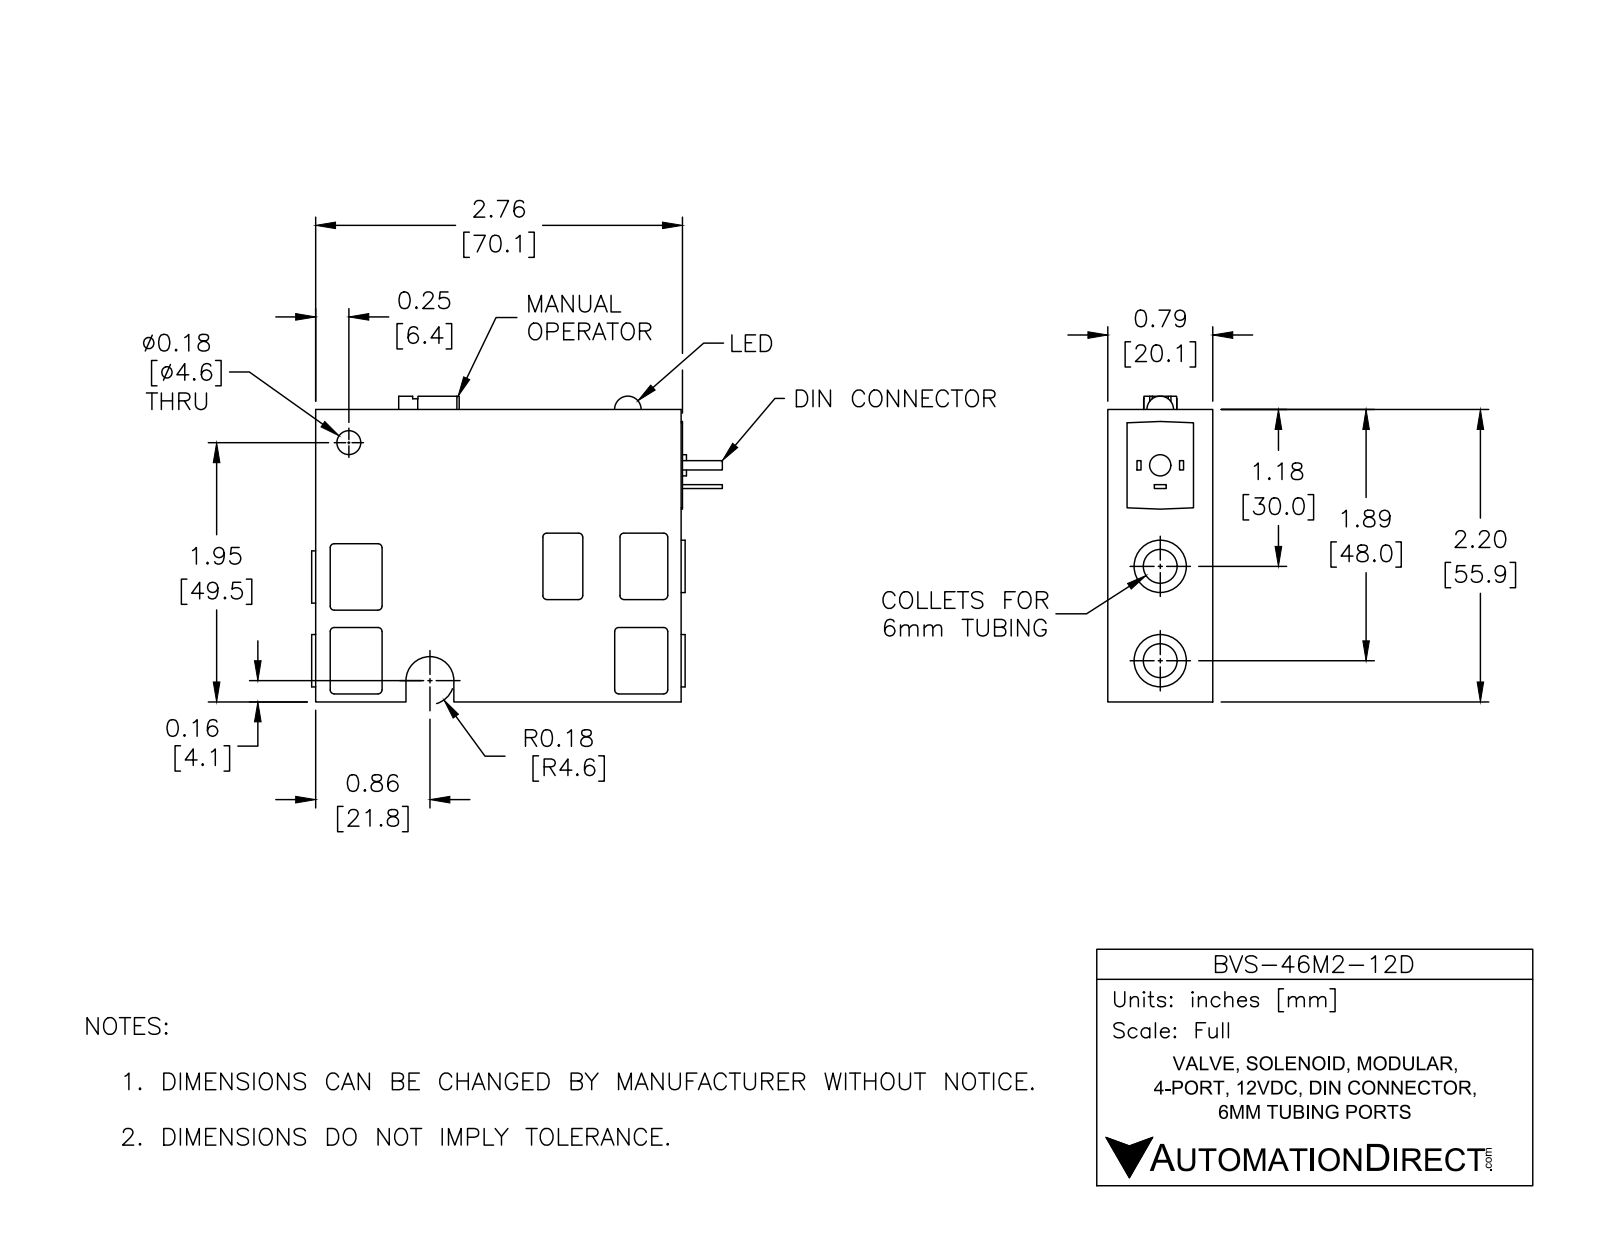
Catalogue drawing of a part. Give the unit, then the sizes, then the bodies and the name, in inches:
Units: inches
Overall size (bounding box): 3.09 × 2.3 × 0.79
Round holes (diameter × count): ⌀0.254 ×3, ⌀0.1 ×1, ⌀0.18 ×1
Round bosses / shafts (diameter × count): ⌀0.394 ×3, ⌀0.16 ×1
Partial cylindrical surfaces — rounded edges, fillets, slot ends (radius × count): R0.03 ×20, R0.02 ×2, R0.125 ×1, R0.18 ×1
Main face-to-face distances: 0.79, 0.1, 2.2, 0.69, 2.75, 0.59, 0.5, 0.11, 2.65, 0.03
Hole centre spacings: 0.08, 0.55, 0.63, 0.63, 0.71, 1.26
Volume: 4.374 in³ · Surface area: 25.19 in²
Bodies: 1 solid, 169 faces (99 planar, 68 cylindrical, 2 other)
Part name (STEP PRODUCT): BVS-46M2-12D
STEP written by: SolidWorks 2016 (AUTOMOTIVE_DESIGN)
